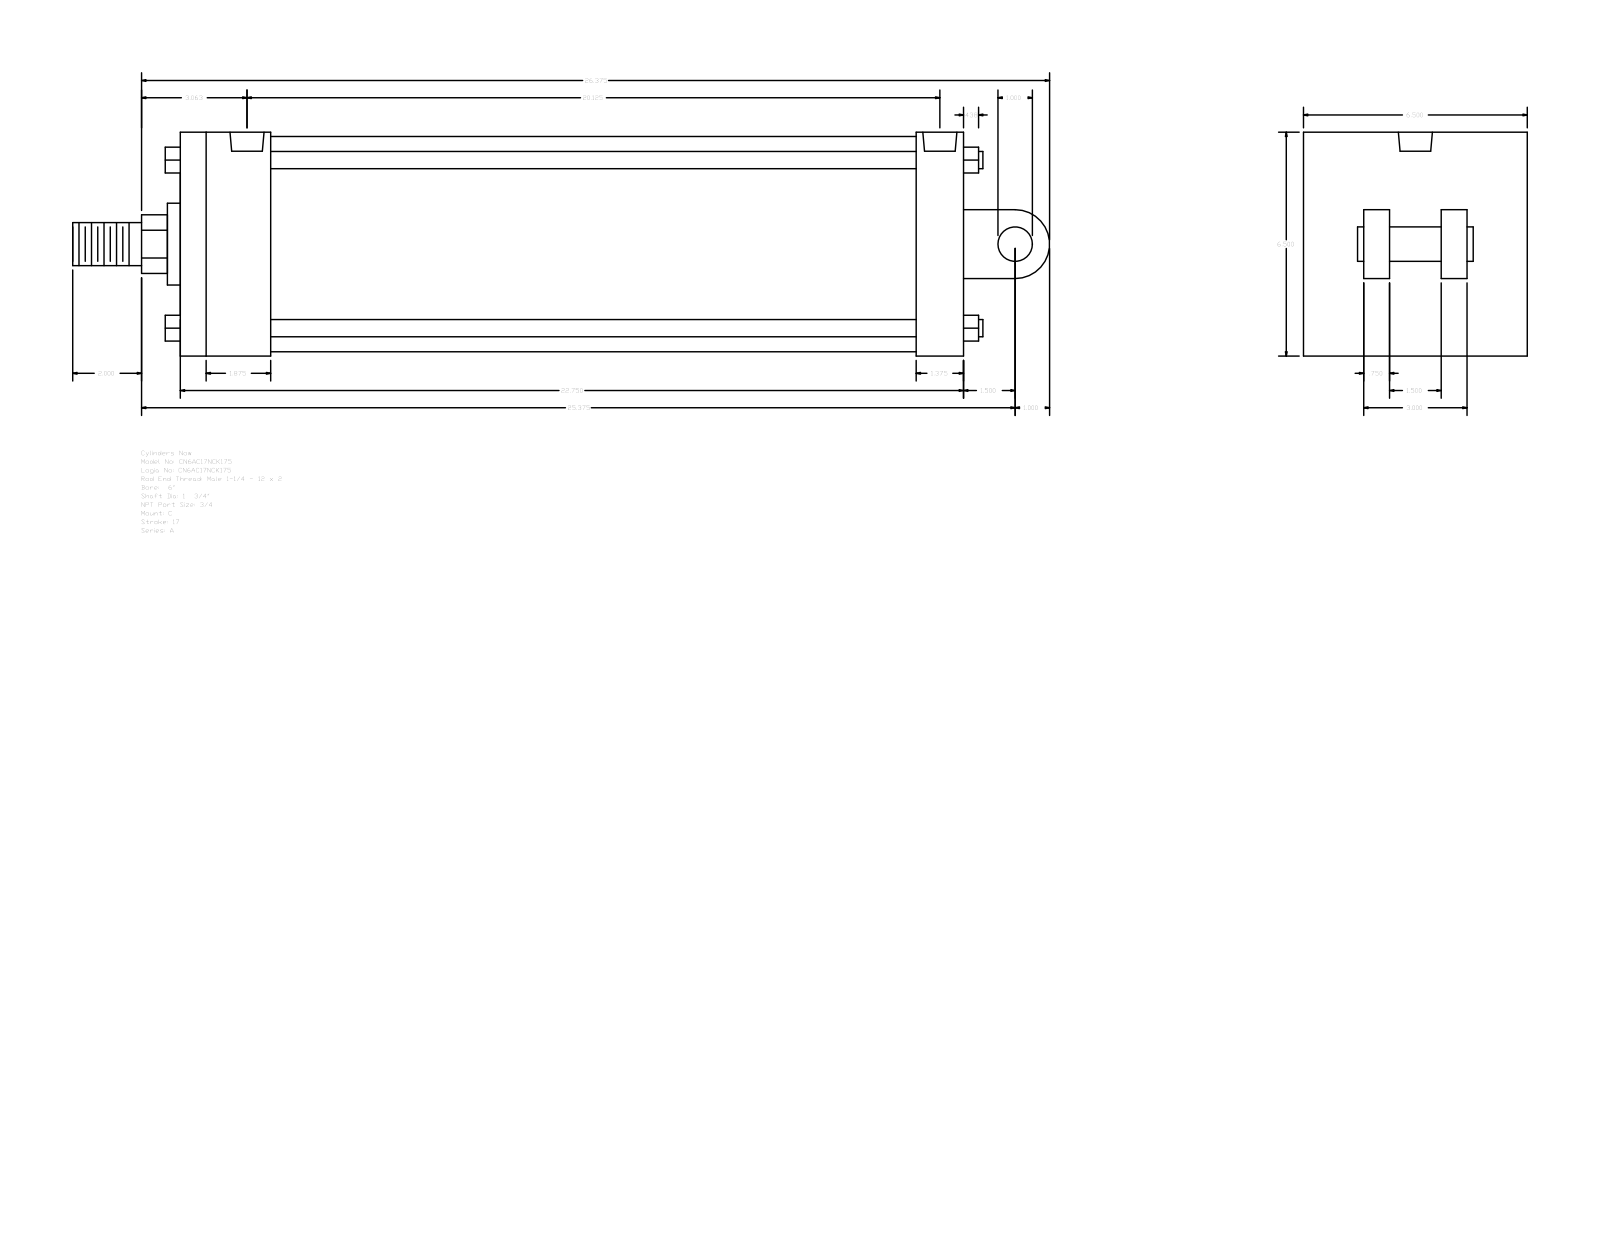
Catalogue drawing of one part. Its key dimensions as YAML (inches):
part_name: "A_C__0600_1.75"
step_written_by: "GSSL Pune (CONFIG_CONTROL_DESIGN)"
units: inches
bodies: {solids: 0, faces: 135, planar: 102, cylindrical: 33, other: 0}
overall_size: [28.375, 6.5, 6.5]
round_holes:
  - {diameter: 0.594, count: 4}
  - {diameter: 0.989, count: 2}
round_bosses_or_shafts:
  - {diameter: 0.5, count: 4}
  - {diameter: 6.25, count: 1}
  - {diameter: 2.375, count: 1}
  - {diameter: 1.75, count: 1}
  - {diameter: 1.25, count: 1}
  - {diameter: 1, count: 1}
partial_cylinders:
  - {radius: 0.852, count: 1}
  - {radius: 1, count: 1}
face_to_face_distances: [6.5, 22.75, 0.75, 2.25, 2.625, 20.125, 21.375, 18.75, 1.375, 2.5]
hole_center_spacings: [0.219, 19.687, 19.906, 20.125]
